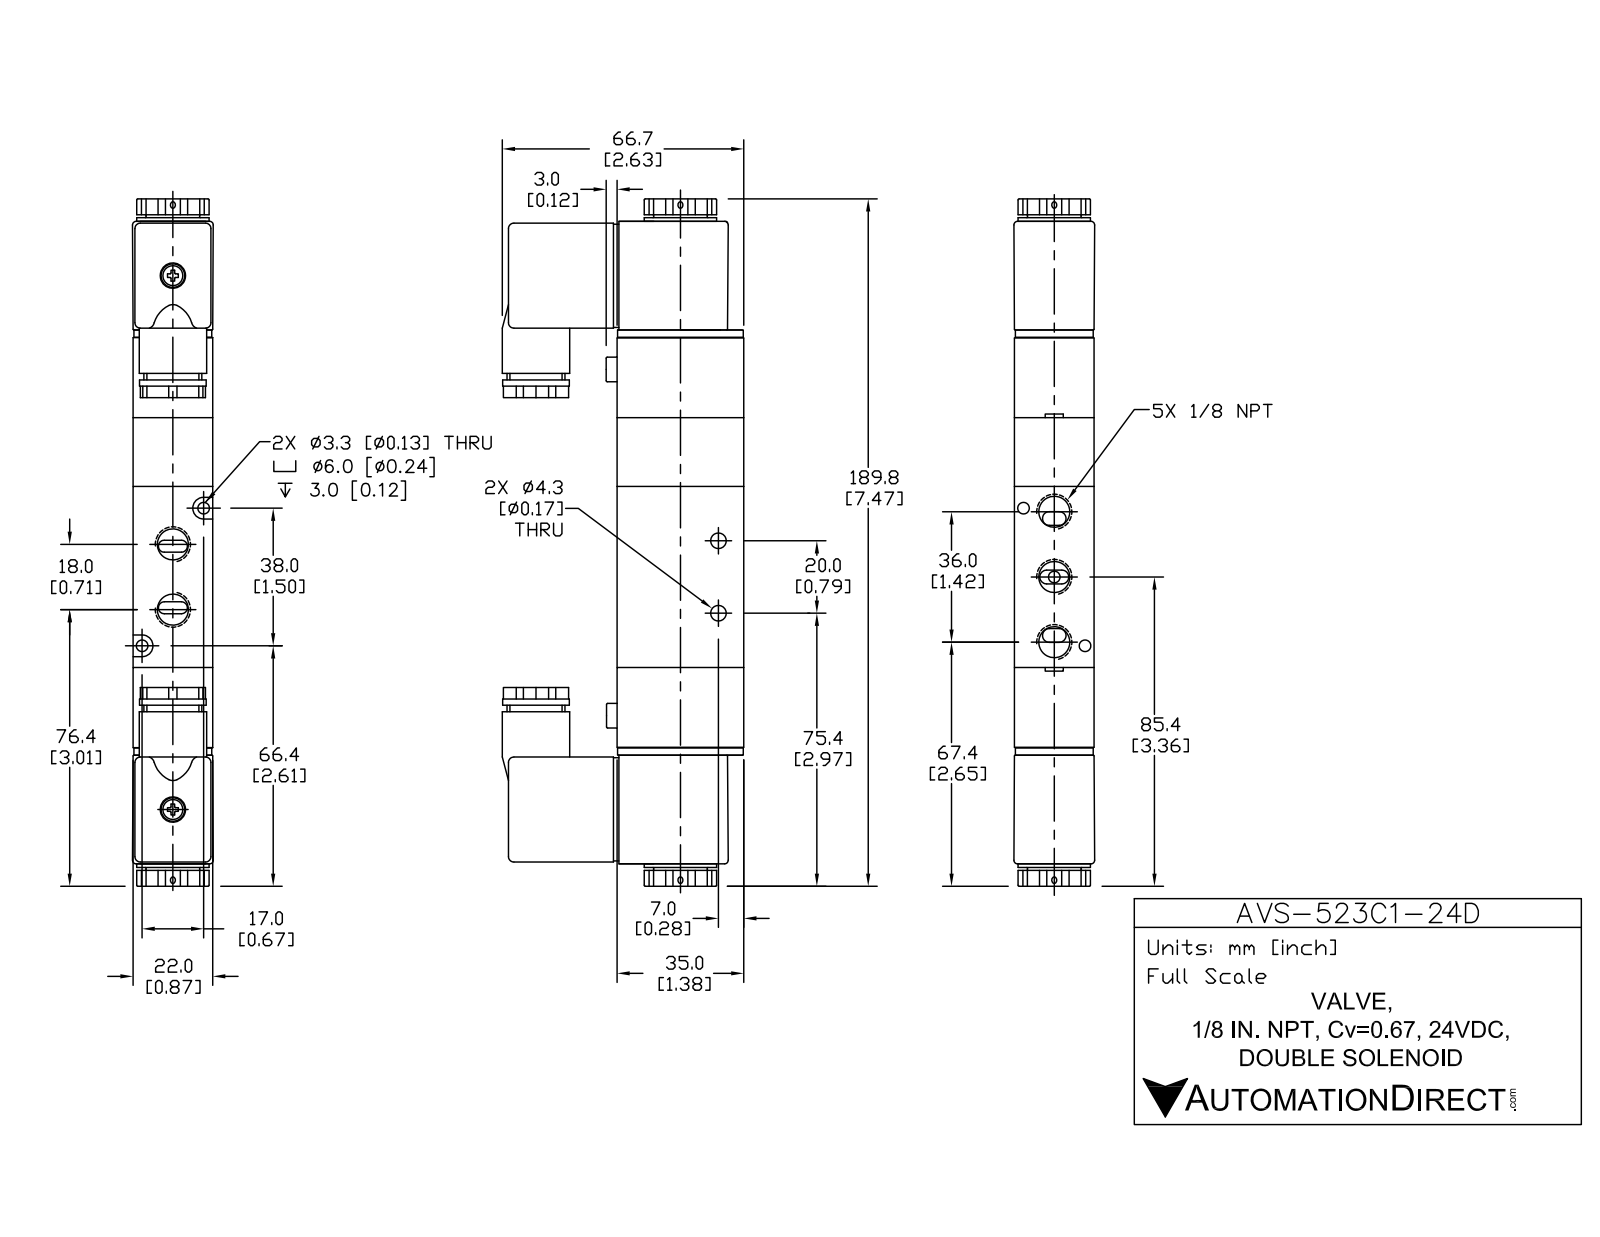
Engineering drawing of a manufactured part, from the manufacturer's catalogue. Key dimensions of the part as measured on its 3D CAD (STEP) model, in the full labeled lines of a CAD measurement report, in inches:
Part name (STEP PRODUCT): AVS-523C1-24D
STEP written by: SolidWorks 2015 (CONFIG_CONTROL_DESIGN)
Units: inches
Bodies: 5 solids, 246 faces (129 planar, 91 cylindrical, 26 other)
Overall size (bounding box): 7.473 × 2.626 × 0.866
Volume: 9.183 in³ · Surface area: 58.14 in²
Round holes (diameter × count): ⌀0.332 ×5, ⌀0.126 ×2, ⌀0.169 ×2, ⌀0.366 ×1
Round bosses / shafts (diameter × count): ⌀0.268 ×2, ⌀0.732 ×1, ⌀0.693 ×1, ⌀0.622 ×1, ⌀0.513 ×1, ⌀0.433 ×1
Partial cylindrical surfaces — rounded edges, fillets, slot ends (radius × count): R0.061 ×10, R0.012 ×8, R0.02 ×8, R0.039 ×8, R0.118 ×2
Main face-to-face distances: 0.035, 0.856, 0.077, 0.789, 0.866, 0.713, 0.891, 2.717, 1.204, 0.198
Hole centre spacings: 0.337, 0.709, 0.819, 1.494, 0.297, 0.308, 0.415, 0.415
